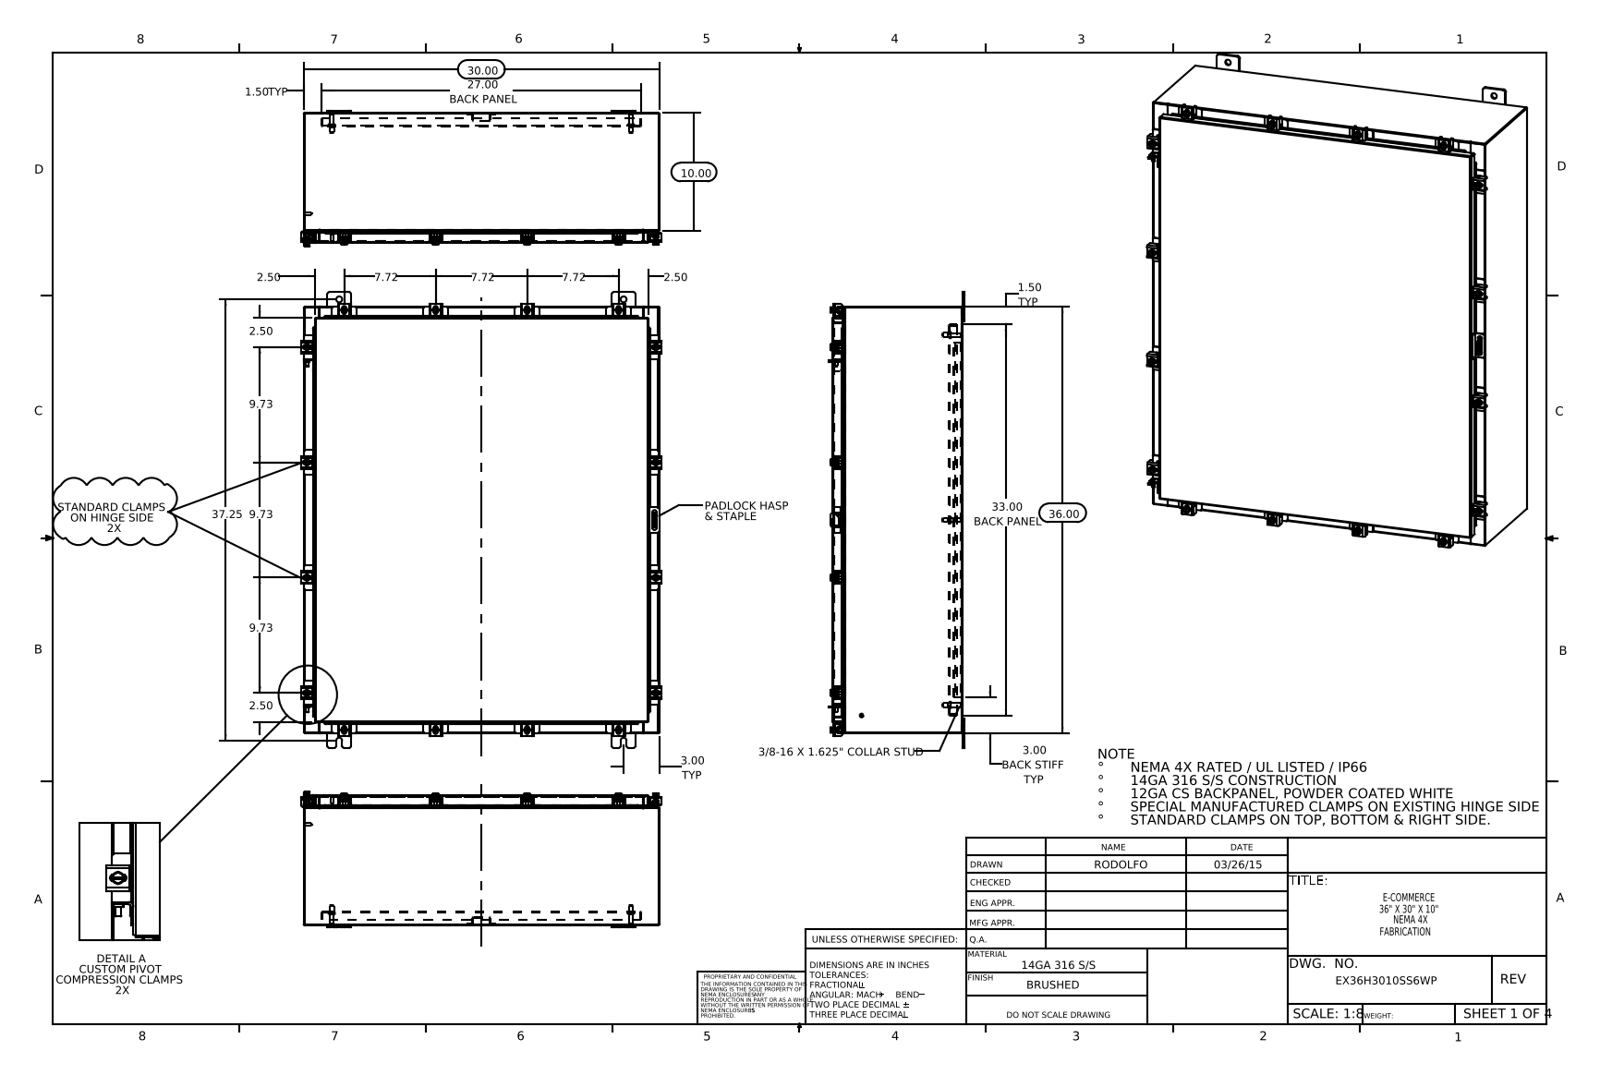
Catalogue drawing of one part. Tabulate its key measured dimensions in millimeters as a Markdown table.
| quantity | value |
| --- | --- |
| part name | Clamp Top_RTP31; Special Clamp Assembly; N-WMT04X30402202210-00 22101002; N-WMT04X30402202210-00 22104005_DEFAULT (+8 more) |
| STEP written by | SolidWorks 2014 (CONFIG_CONTROL_DESIGN) |
| units | millimeters |
| bodies | 104 solids, 2594 faces (1371 planar, 1011 cylindrical, 212 other) |
| overall size | 977.9 × 772.7 × 290.9 |
| volume | 6 571 000 mm³ |
| surface area | 6 431 000 mm² |
| round holes (diameter × count) | 5.4 × 16, 6.6 × 16, 12.7 × 10, 3.2 × 1, 6.4 × 1 |
| round bosses / shafts (diameter × count) | 12.7 × 16, 6.4 × 16, 10.1 × 14, 15.9 × 6, 9.5 × 6, 8.4 × 6, 8 × 2, 6 × 2 |
| partial cylindrical surfaces (radius × count) | 1.5 × 70, 3.6 × 32, 0.3 × 30, 3 × 30, 2.2 × 26, 4.8 × 24, 2.3 × 22, 1.3 × 21 |
| main face-to-face distances | 1.9, 276.9, 275, 278.8, 2.6, 25.4, 27.3, 249.6, 251.5, 29.9 |
| hole center spacings | 787.8, 59.6, 112.8, 134.6, 247.1, 278.5, 336.3, 374.5 |
